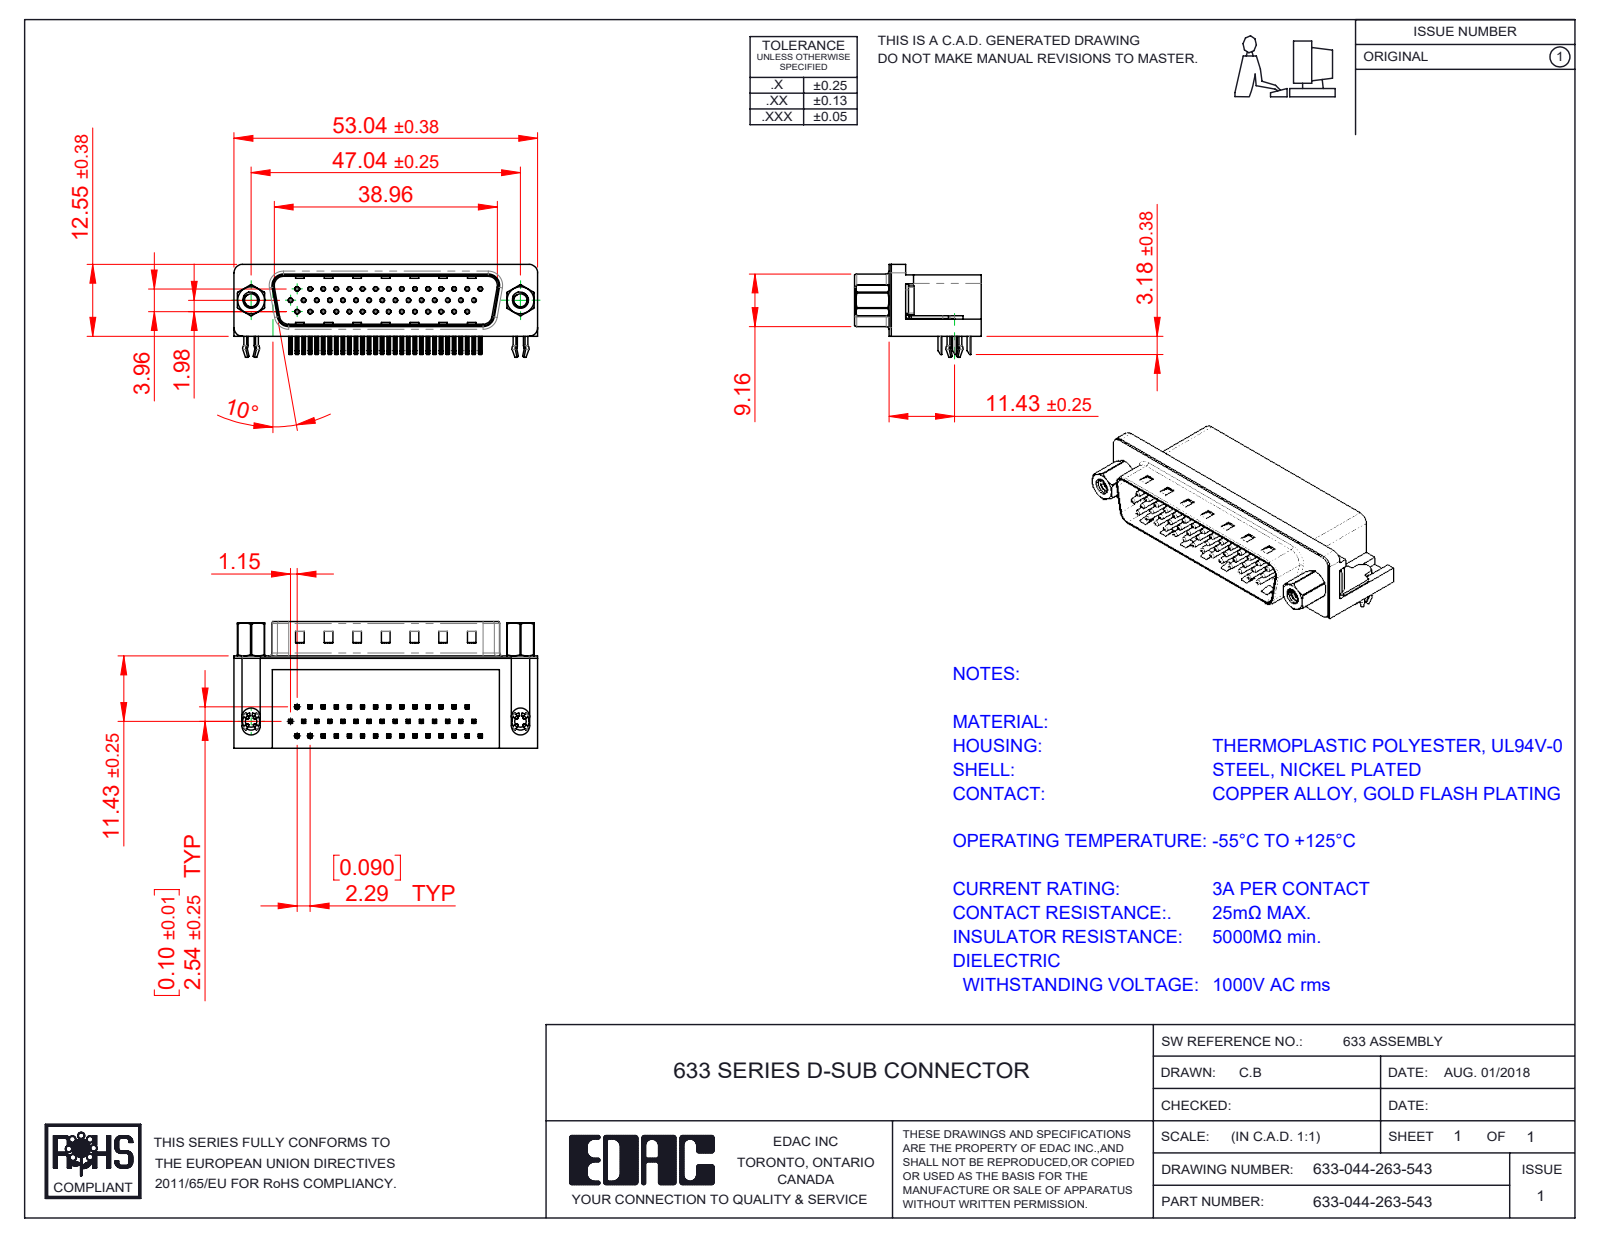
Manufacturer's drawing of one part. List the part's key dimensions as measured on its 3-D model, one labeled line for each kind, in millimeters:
Part name (STEP PRODUCT): 633 Contact Middle; 633 Contact Bottom; 633 Shell_44 Contact; 633 Housing_44 Contact (+5 more)
STEP written by: SolidWorks 2016 (CONFIG_CONTROL_DESIGN)
Units: millimetres
Bodies: 52 solids, 3930 faces (2381 planar, 1130 cylindrical, 419 other)
Overall size (bounding box): 53.04 × 22.1 × 16.25
Volume: 8 326 mm³ · Surface area: 10 746 mm²
Round holes (diameter × count): ⌀0.35 ×44, ⌀0.8 ×44, ⌀2 ×2, ⌀2.26 ×2, ⌀2.29 ×2, ⌀4 ×2, ⌀4.8 ×2, ⌀5 ×2
Round bosses / shafts (diameter × count): ⌀0.75 ×44, ⌀4.9 ×2, ⌀4.75 ×2, ⌀3.9 ×2, ⌀3 ×2, ⌀2.79 ×2
Partial cylindrical surfaces — rounded edges, fillets, slot ends (radius × count): R0.25 ×188, R0.12 ×88, R1 ×16, R0.5 ×9, R1.6 ×8, R1.5 ×7, R0.9 ×4, R2 ×4
Main face-to-face distances: 0.4, 10.35, 15.7, 8.76, 2.9, 2.5, 16.1, 2.1, 10.7, 2.54
Hole centre spacings: 2.29, 4.57, 4.58, 2.28, 6.87, 9.16, 11.45, 2.27
